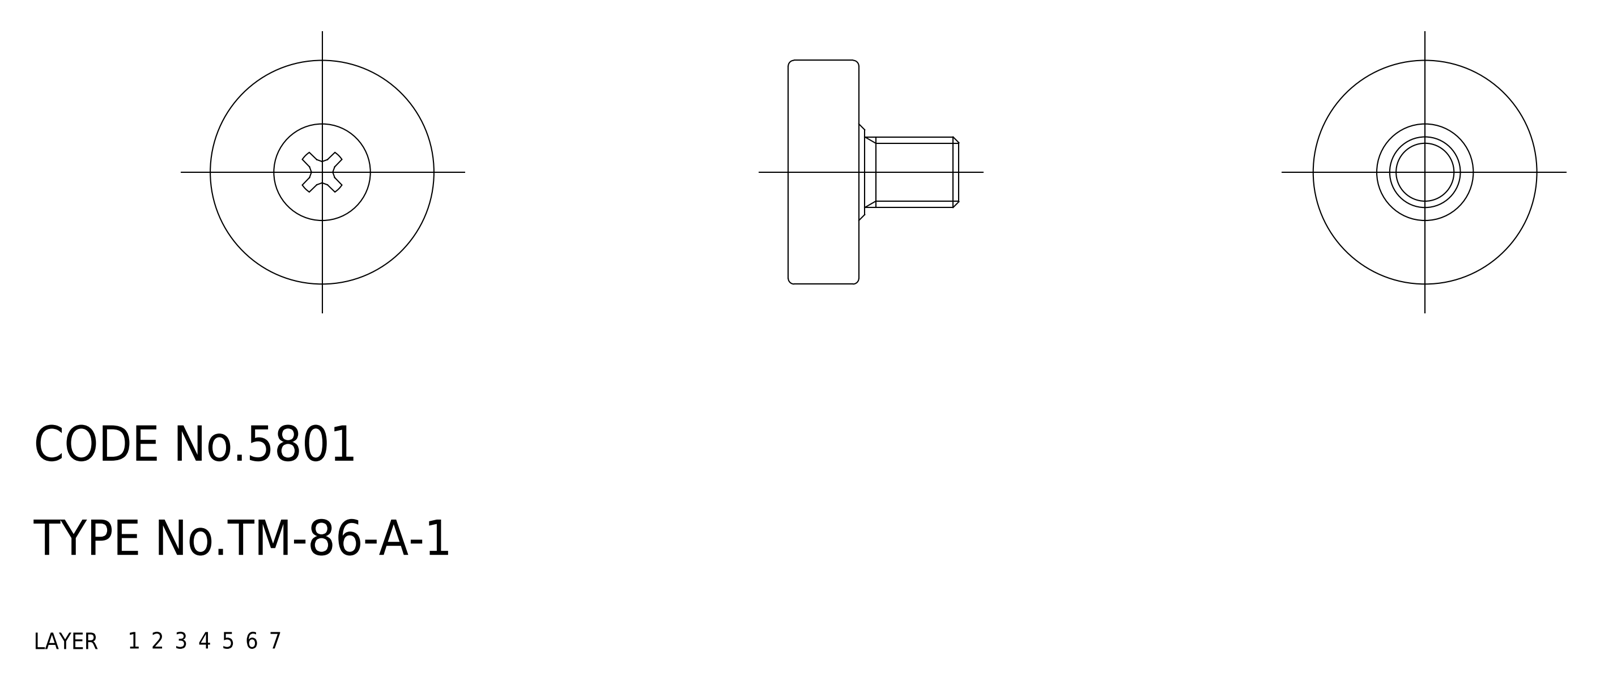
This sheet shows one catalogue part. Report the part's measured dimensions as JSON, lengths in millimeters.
{"part_name": "roller", "step_written_by": "CADfix (AUTOMOTIVE_DESIGN)", "units": "millimeters", "bodies": {"solids": 1, "faces": 49, "planar": 0, "cylindrical": 0, "other": 49}, "overall_size": [19, 19, 14.5], "volume_mm3": 1932, "surface_area_mm2": 1458}
